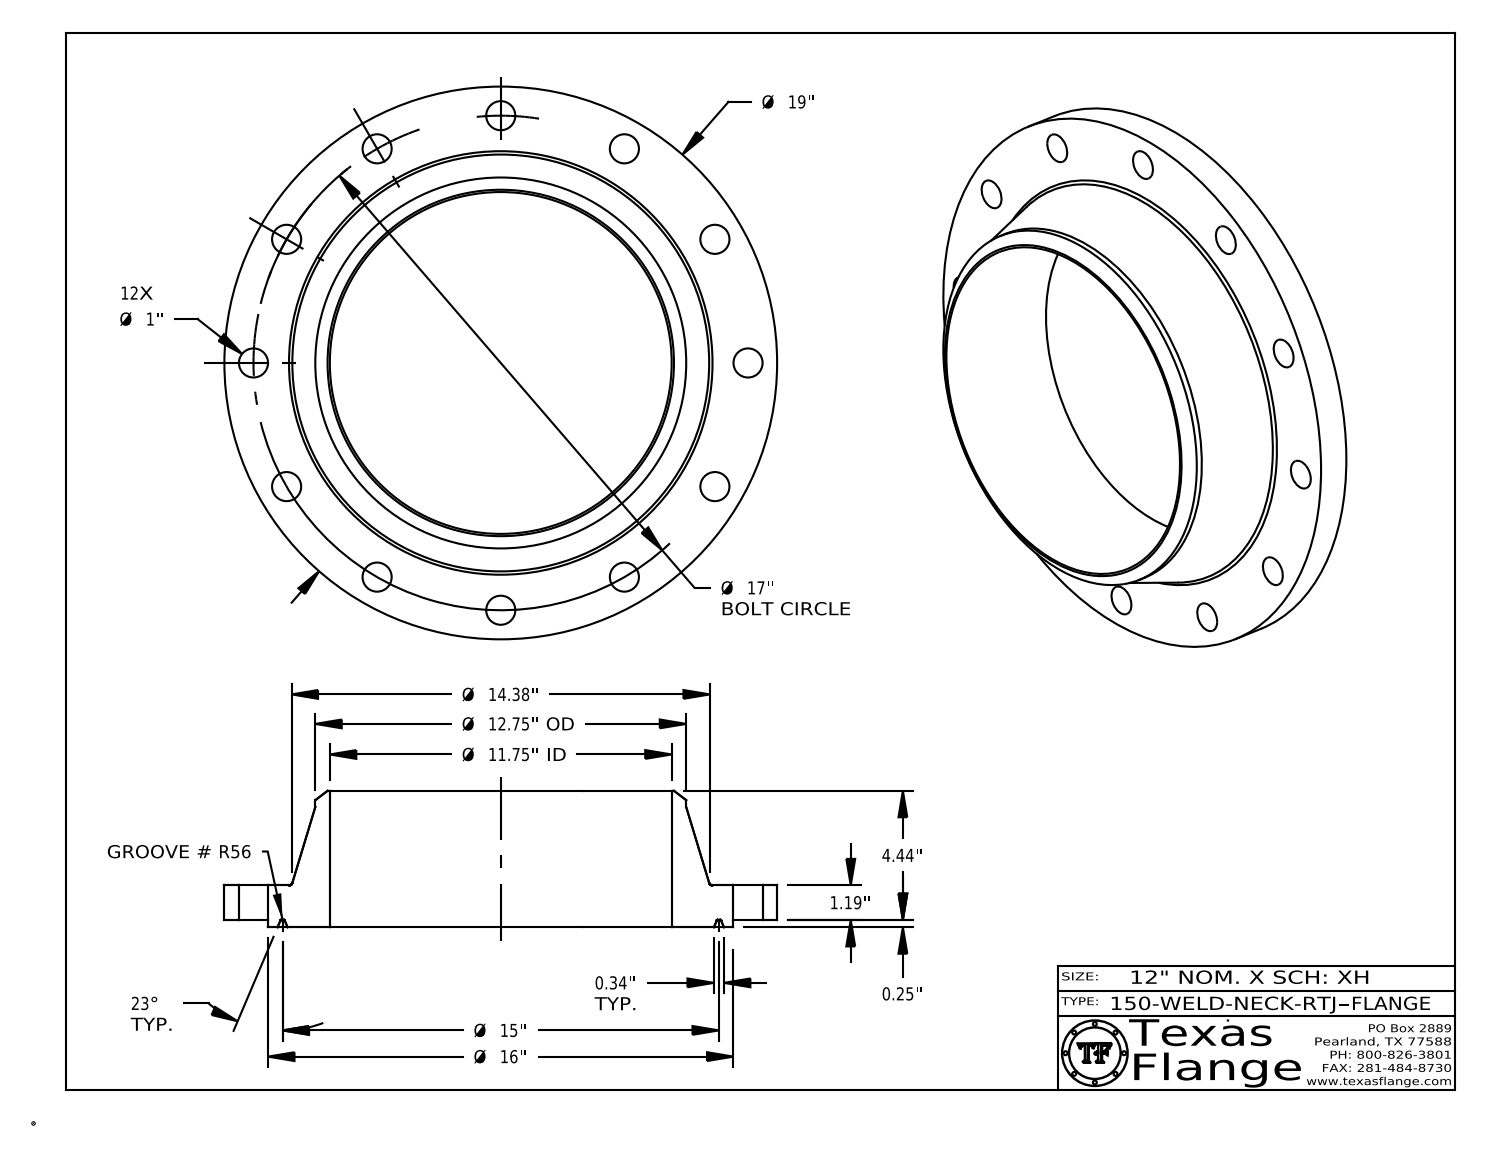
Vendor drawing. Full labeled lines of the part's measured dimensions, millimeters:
Part name (STEP PRODUCT): 150-WELD-NECK-RTJ
STEP written by: CATIA V5 STEP AP214 (AUTOMOTIVE_DESIGN)
Units: millimetres
Bodies: 1 solid, 437 faces (371 planar, 52 cylindrical, 14 other)
Overall size (bounding box): 482.6 × 482.6 × 119.1
Volume: 5 296 000 mm³ · Surface area: 481 200 mm²
Round holes (diameter × count): ⌀25.4 ×12, ⌀12.6 ×1, ⌀298.5 ×1
Round bosses / shafts (diameter × count): ⌀0.8 ×8, ⌀482.6 ×1, ⌀406.4 ×1, ⌀323.9 ×1, ⌀9.9 ×1
Main face-to-face distances: 30.2, 6.4, 36.6, 119.1, 112.8, 82.6, 36.4, 30.1, 82.7, 3.8
Hole centre spacings: 215.9, 417.1, 111.8, 305.3, 373.9, 111.8, 305.3, 373.9
